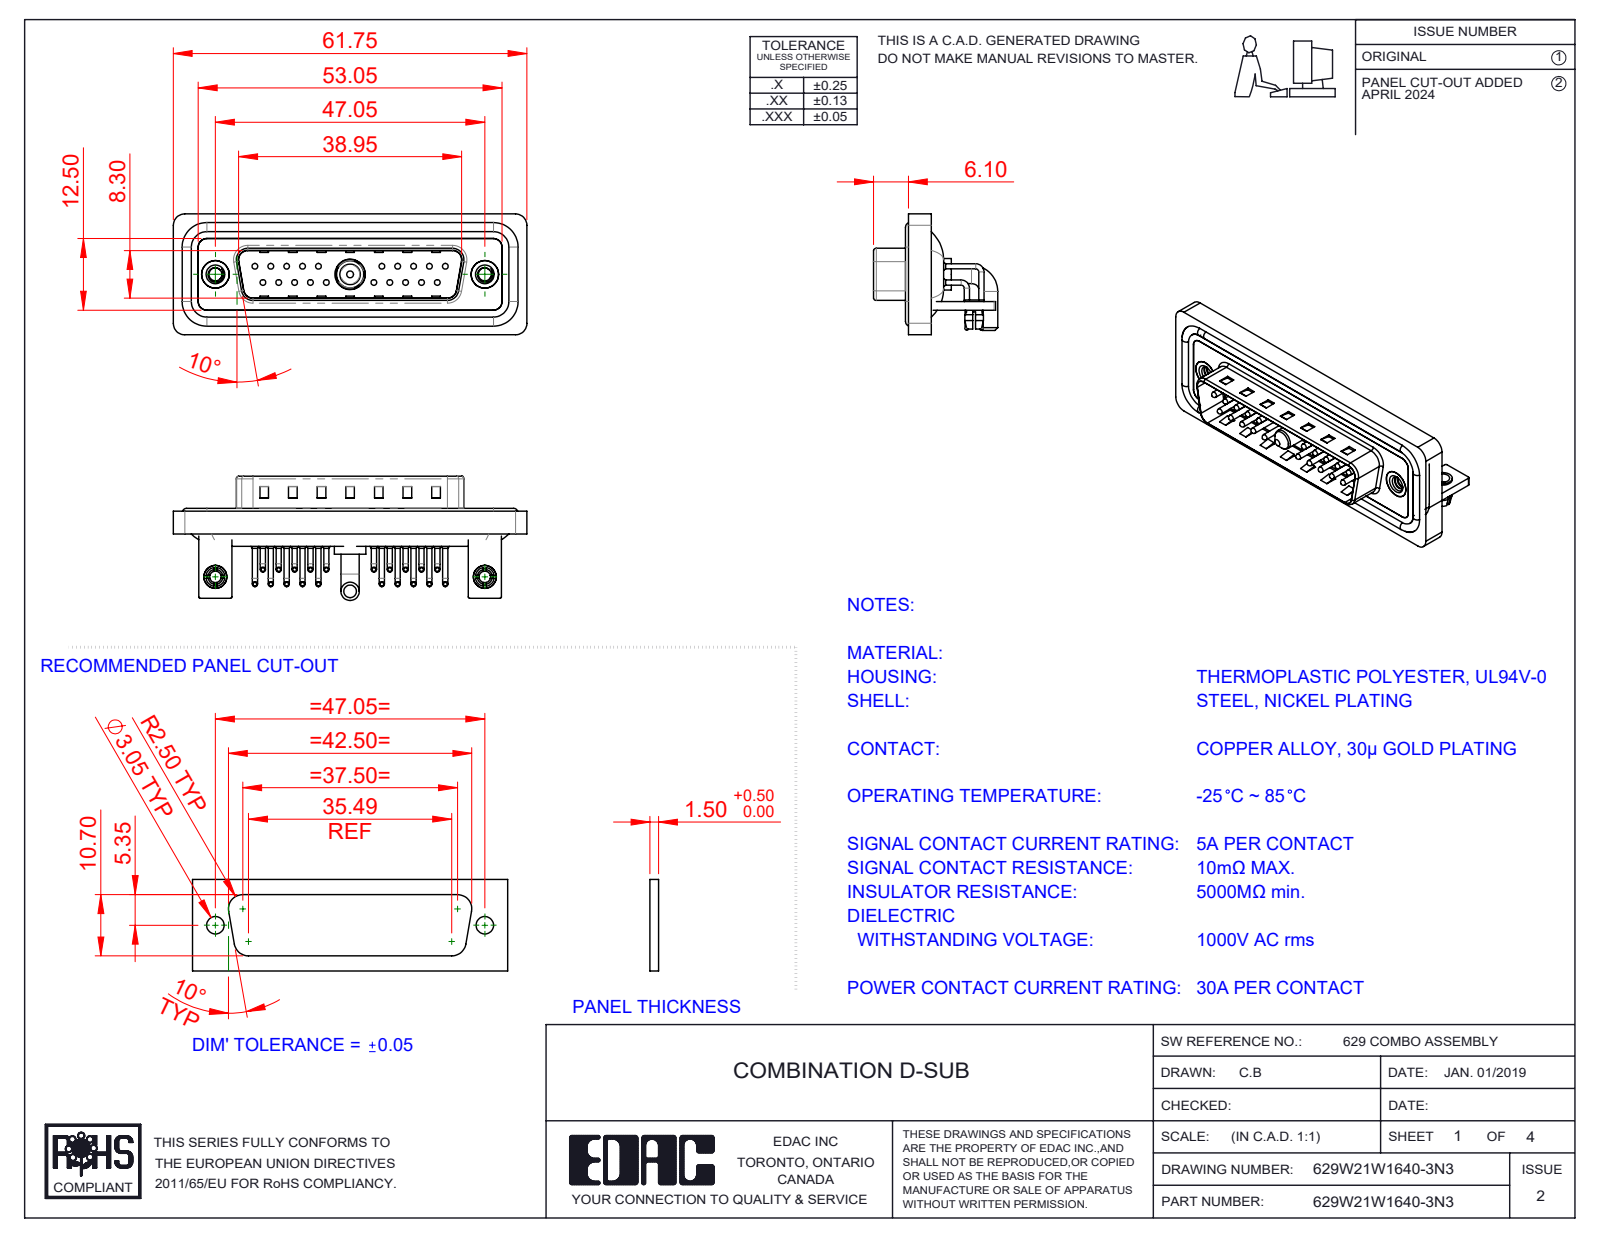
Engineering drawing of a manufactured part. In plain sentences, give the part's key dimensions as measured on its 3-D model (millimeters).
The part is named "629Combo Board Lock; 629W21W1640-3N3; 629Combo Shell Front_25 Contacts; 629Combo Threaded Rivet_3 (+7 more)". Its 3-D file was written by "SolidWorks 2023 (CONFIG_CONTROL_DESIGN)". It is 33 solids with 2858 faces: 1567 planar, 979 cylindrical and 312 other. Overall it measures 61.75 by 21.7 by 21.1 millimeters. Its volume is 7 760 cubic millimeters and its surface area 13 537 square millimeters. Round holes: 22 of diameter 2, 20 of diameter 0.75, 20 of diameter 1.6, 2 of diameter 2.26, 2 of diameter 2.5, 2 of diameter 3.2, 2 of diameter 4, 2 of diameter 4.8, 2 of diameter 5, 1 of diameter 4.85, 1 of diameter 5.3. Round bosses or shafts: 40 of diameter 0.9, 20 of diameter 1.5, 20 of diameter 1, 20 of diameter 0.65, 4 of diameter 1.6, 2 of diameter 4.9, 2 of diameter 4, 2 of diameter 3.4. Partial cylindrical surfaces (rounded edges, fillets, slot ends): 20 of radius 1.01, 19 of radius 2, 18 of radius 1.5, 16 of radius 0.25, 9 of radius 0.5, 8 of radius 1.6, 4 of radius 0.6, 4 of radius 0.65. The main face-to-face distances are 0.4, 0.8, 2.1, 2.9, 1.5, 1.1, 4.1, 1.6, 4.5, 3.7. The hole center spacings are 3.16, 2.77, 5.54, 8.31, 5.04, 19.39, 20.97, 22.16.
